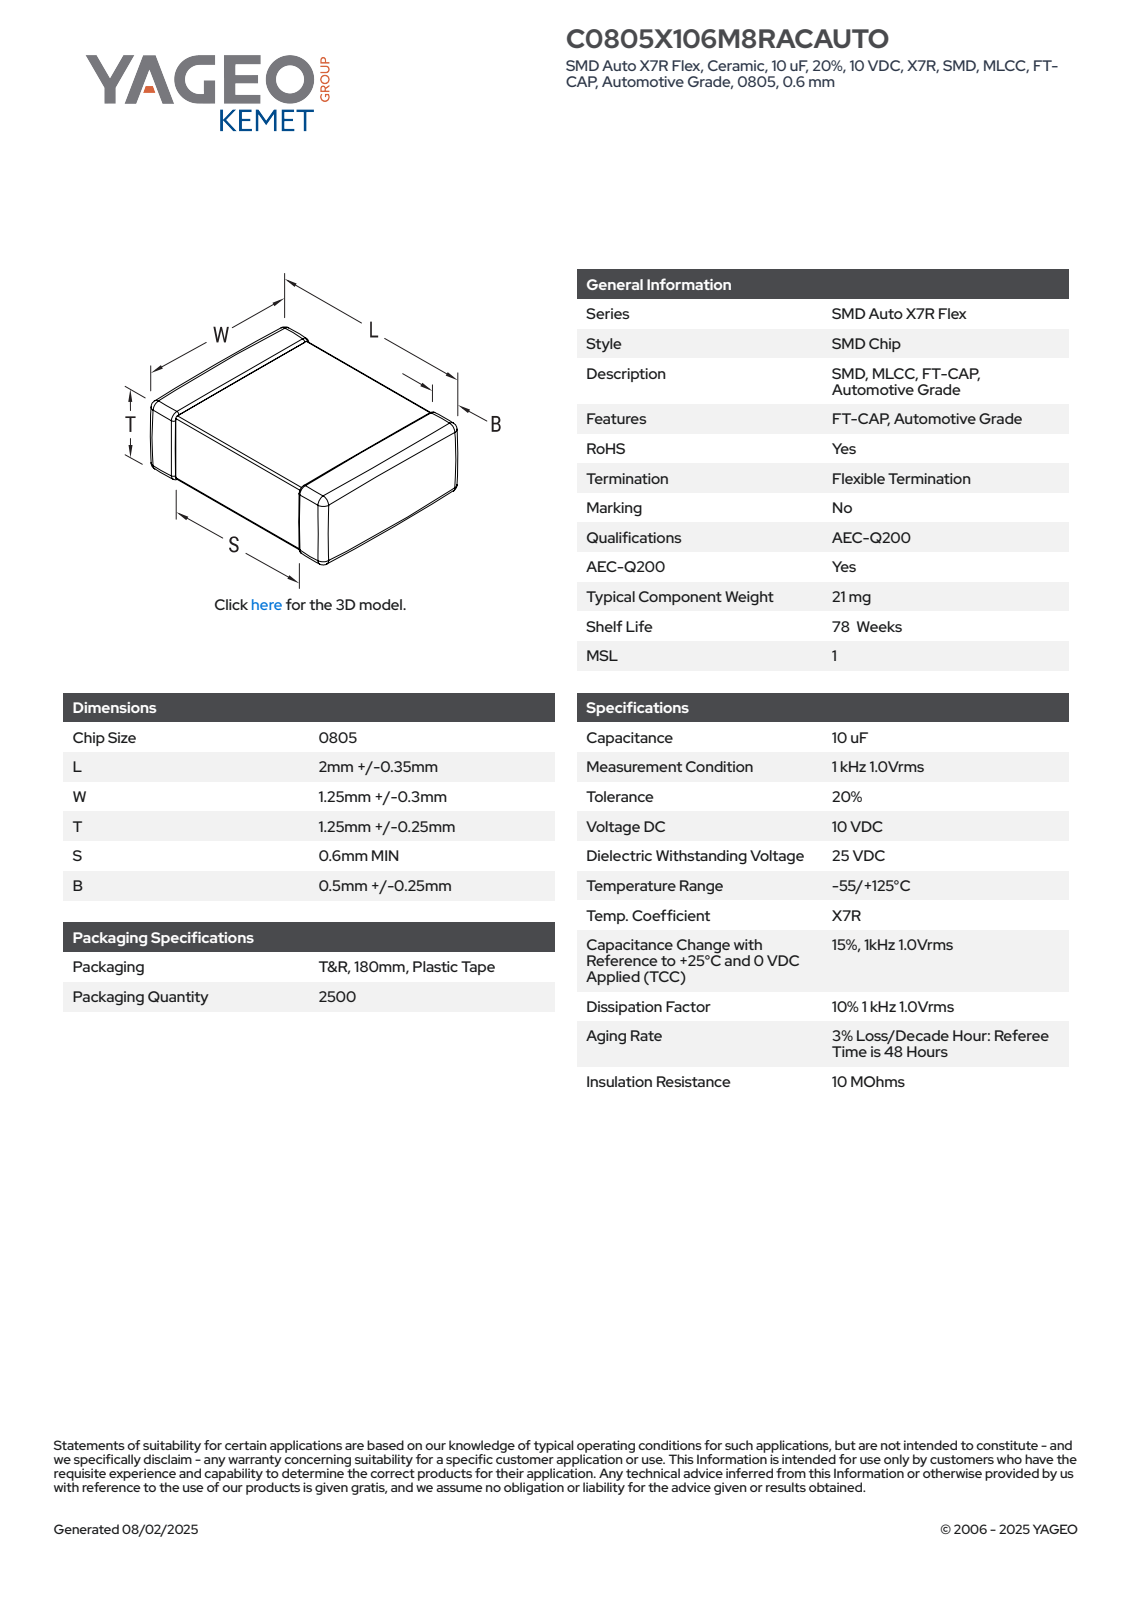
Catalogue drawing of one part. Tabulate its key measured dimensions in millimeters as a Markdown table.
| quantity | value |
| --- | --- |
| part name | CCS_CCSTD_0805_L2.35W1.55T1.5B0.5 |
| STEP written by | SolidWorks 2021 (AUTOMOTIVE_DESIGN) |
| units | millimeters |
| bodies | 4 solids, 125 faces (71 planar, 38 cylindrical, 16 other) |
| overall size | 2.35 × 1.55 × 1.5 |
| volume | 5 mm³ |
| surface area | 19 mm² |
| main face-to-face distances | 1.47, 1.52, 2.35, 1.5, 1.55, 1.44, 1.49, 1.04, 1.31, 1.08 |
